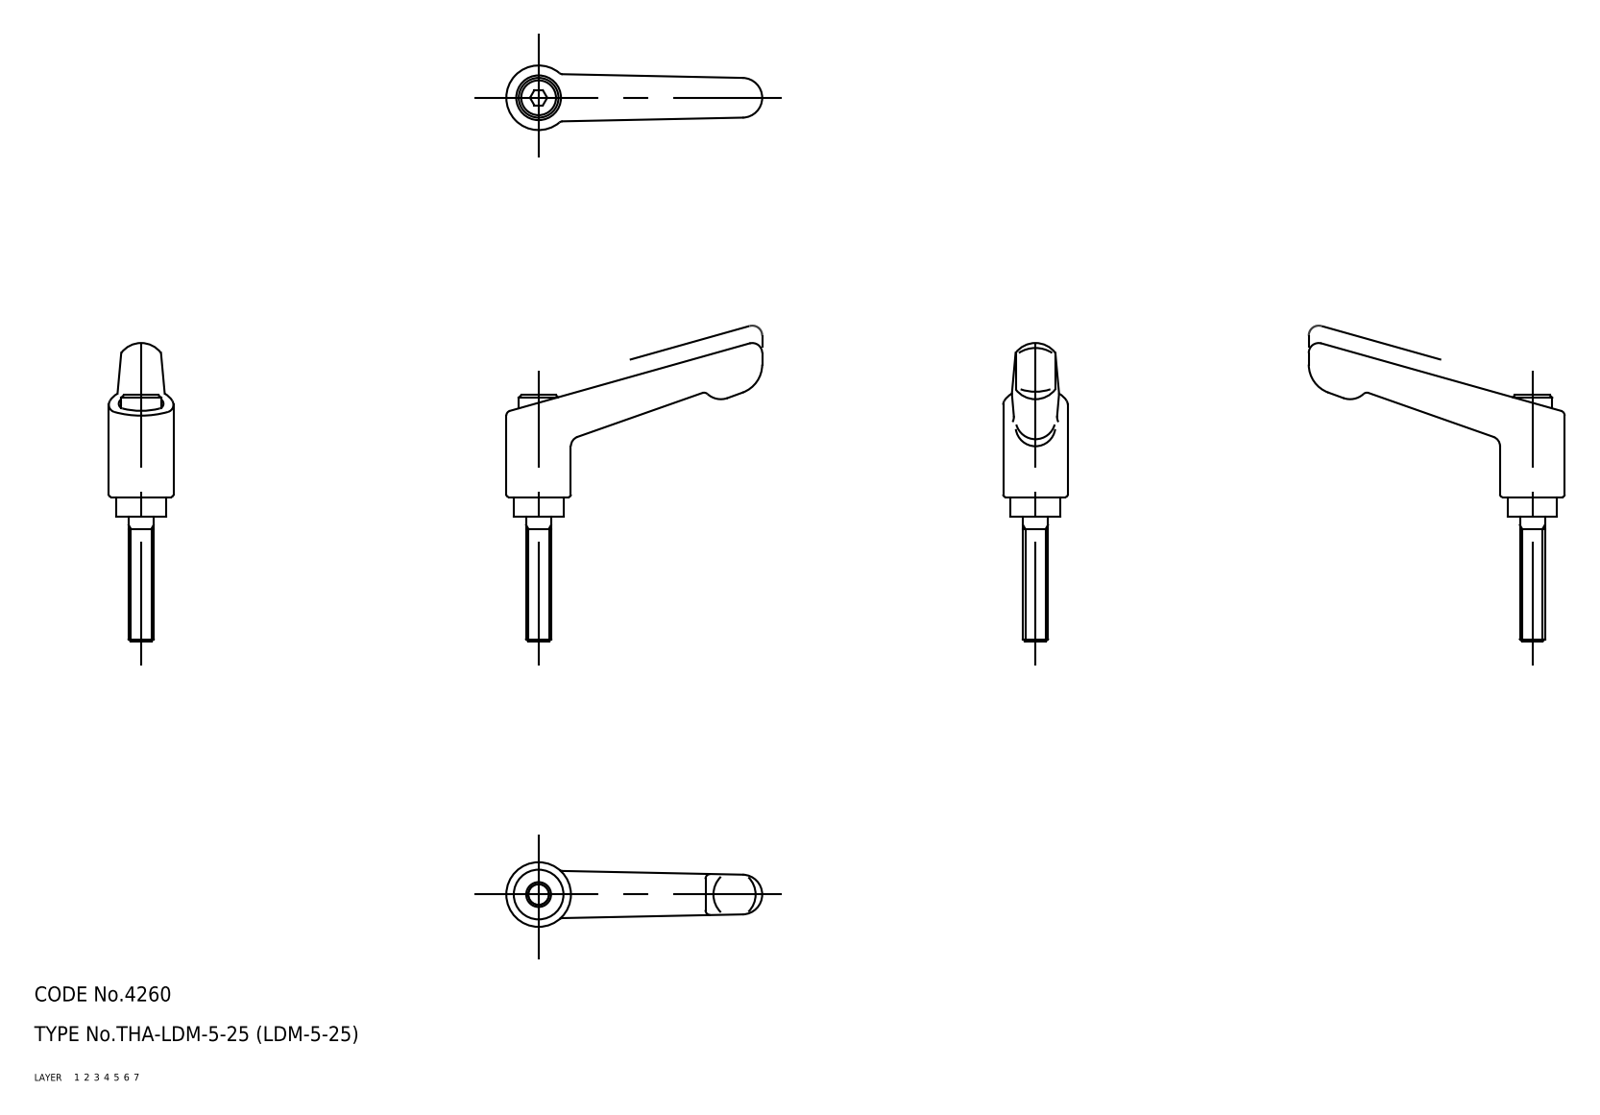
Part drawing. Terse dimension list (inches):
name: sleeve; screw; handle; LDM_5_25_12859_36
written by: CADfix (AUTOMOTIVE_DESIGN)
unit: in
bodies: 3 solids, 70 faces (0 planar, 0 cylindrical, 70 other)
size: 2.362 × 2.028 × 0.512
volume: 0.343 in³; area: 6.061 in²
